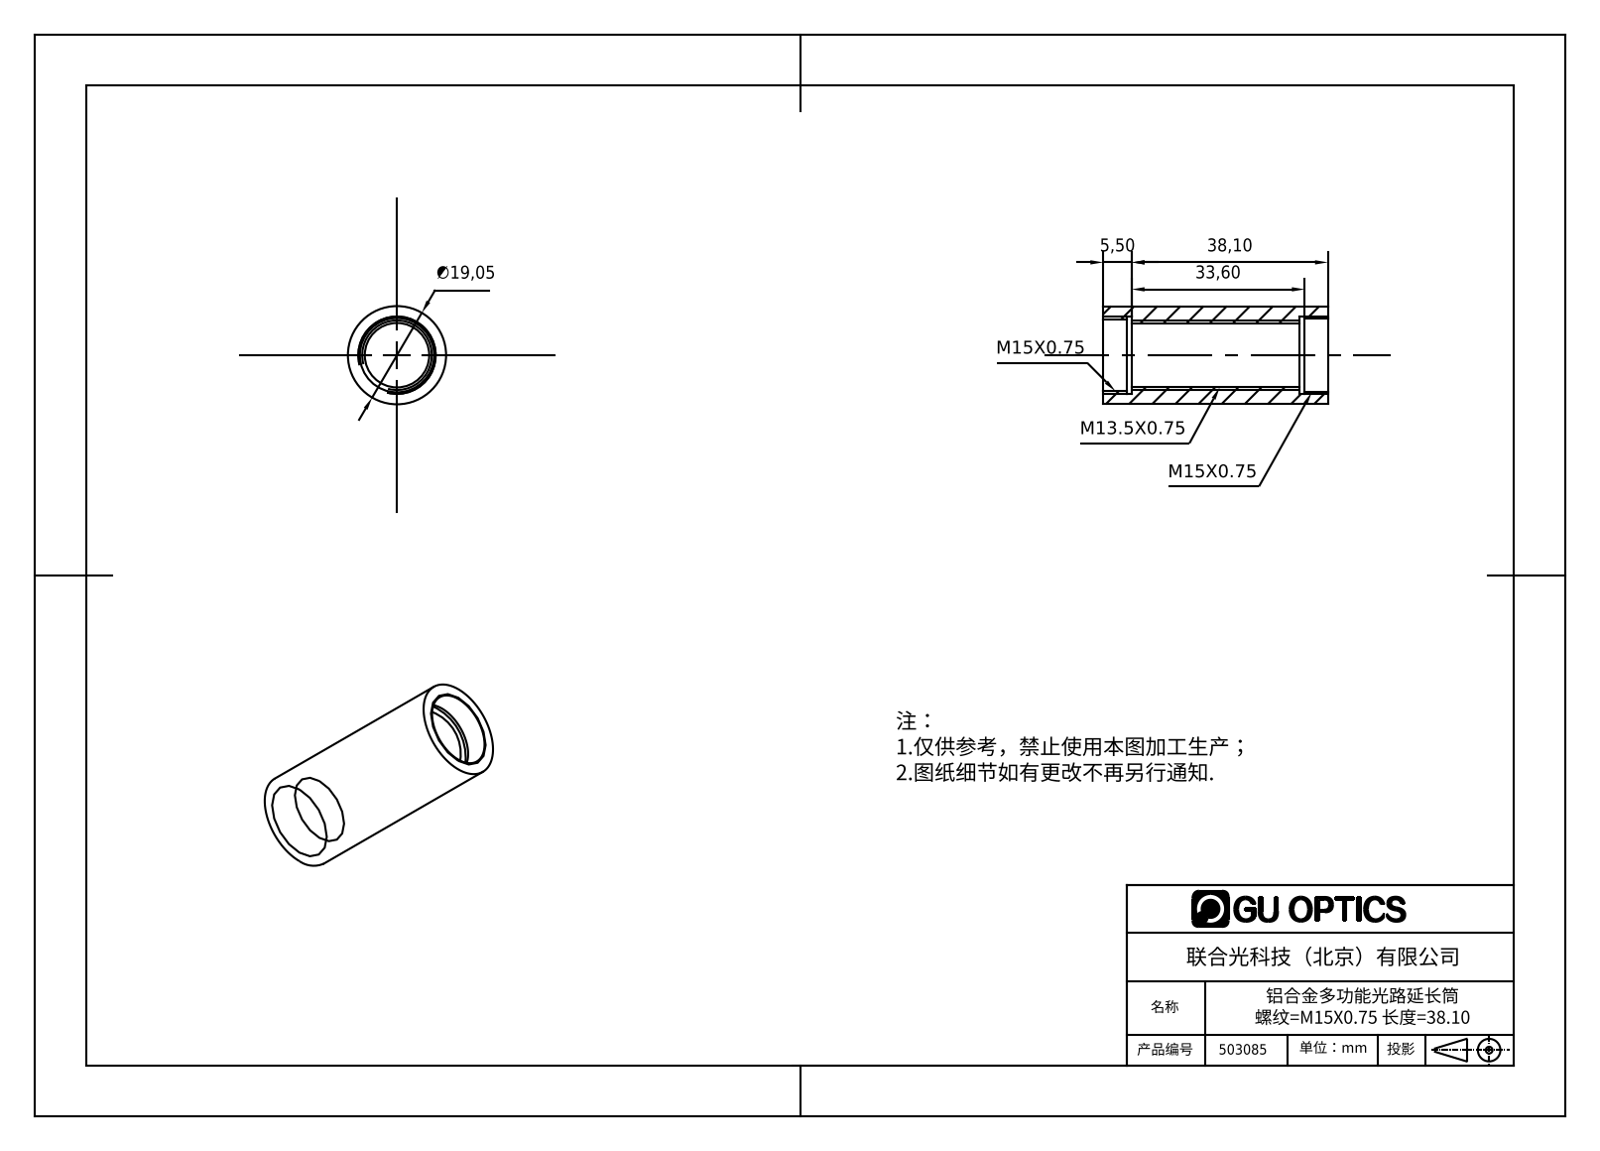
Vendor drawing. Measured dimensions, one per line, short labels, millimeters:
name: 503085
written by: SolidWorks 2016 (AUTOMOTIVE_DESIGN)
unit: mm
bodies: 1 solid, 18 faces (6 planar, 12 cylindrical, 0 other)
size: 43.6 × 19.05 × 19.05
volume: 6 638 mm³; area: 4 803 mm²
holes: 1× ⌀12.5, 1× ⌀14, 1× ⌀14.4, 1× ⌀15.2
bosses: 1× ⌀19.05
face distances: 43.6, 5.5, 38.1, 32.6, 4.5, 39.1, 1, 33.6, 34.6
